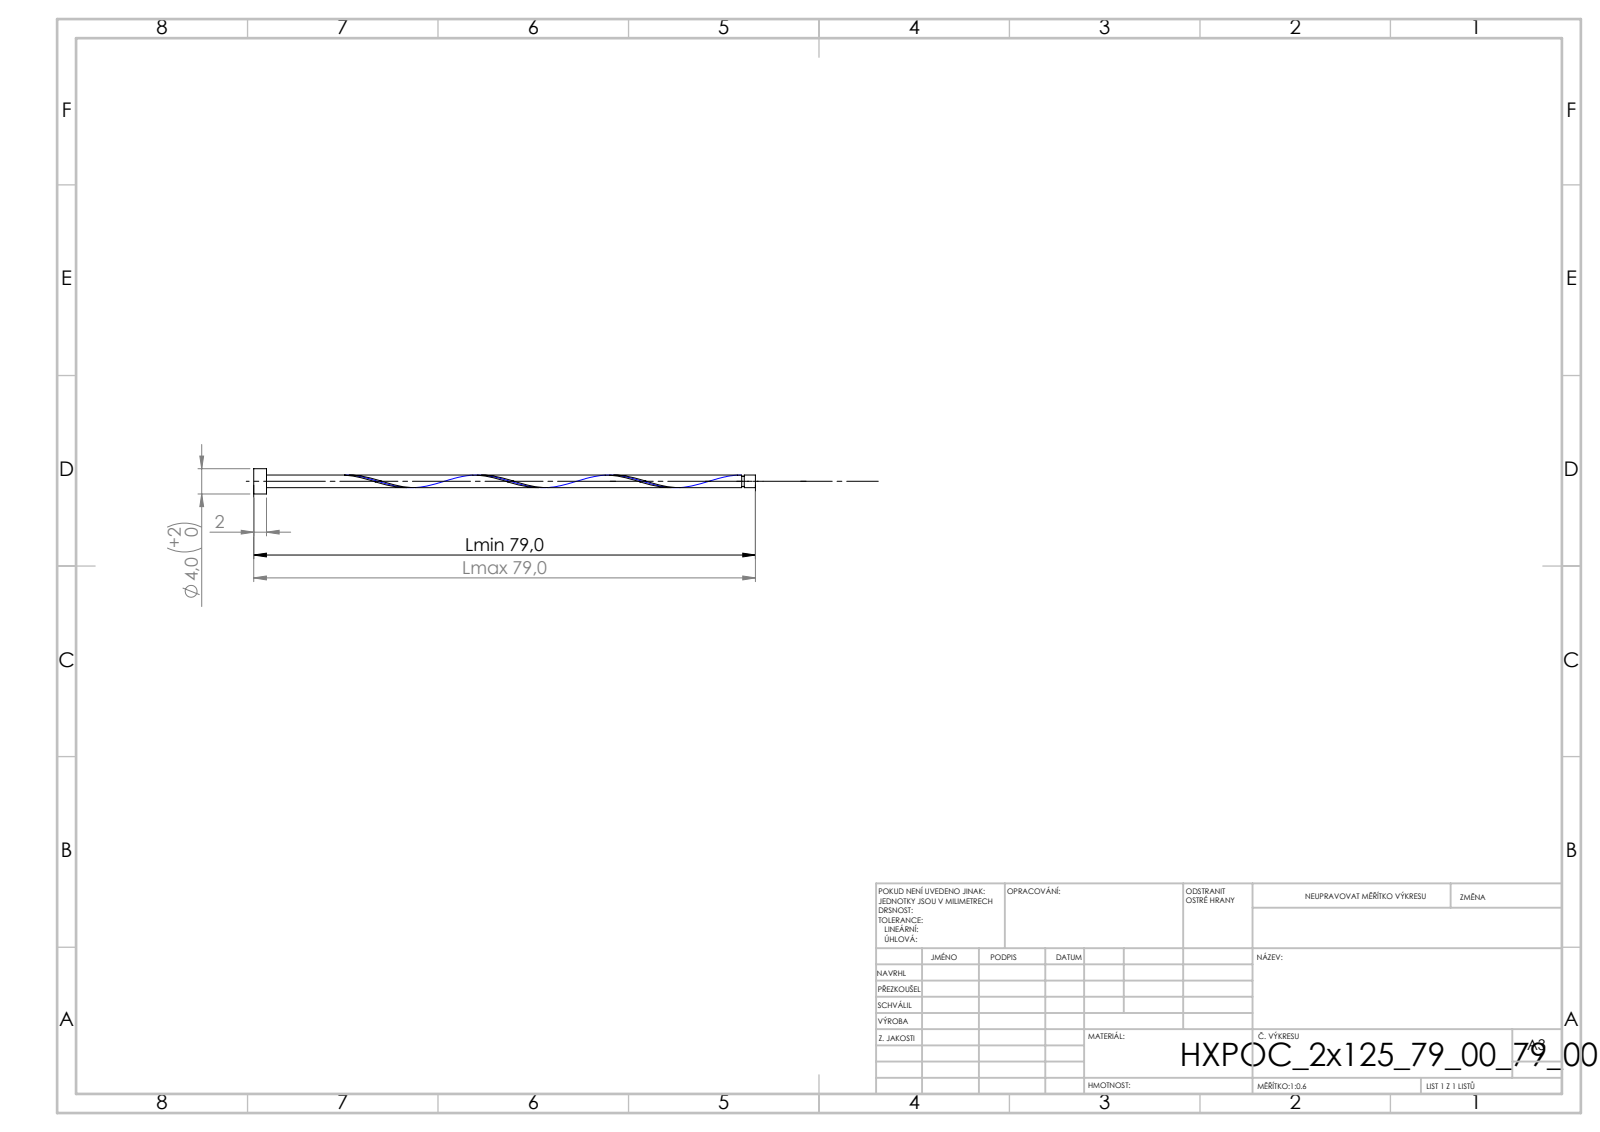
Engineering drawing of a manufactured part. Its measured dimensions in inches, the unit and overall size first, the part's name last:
Units: inches
Overall size (bounding box): 3.11 × 0.157 × 0.157
Round bosses / shafts (diameter × count): ⌀0.157 ×1, ⌀0.079 ×1, ⌀0.063 ×1
Main face-to-face distances: 0.079, 3.11, 3.031, 3.041, 2.963, 0.069, 3.026, 2.947, 0.016, 0.085
Volume: 0.021 in³ · Surface area: 1.26 in²
Bodies: 1 solid, 16 faces (6 planar, 9 cylindrical, 1 other)
STEP written by: SolidWorks 2019 (CONFIG_CONTROL_DESIGN)
